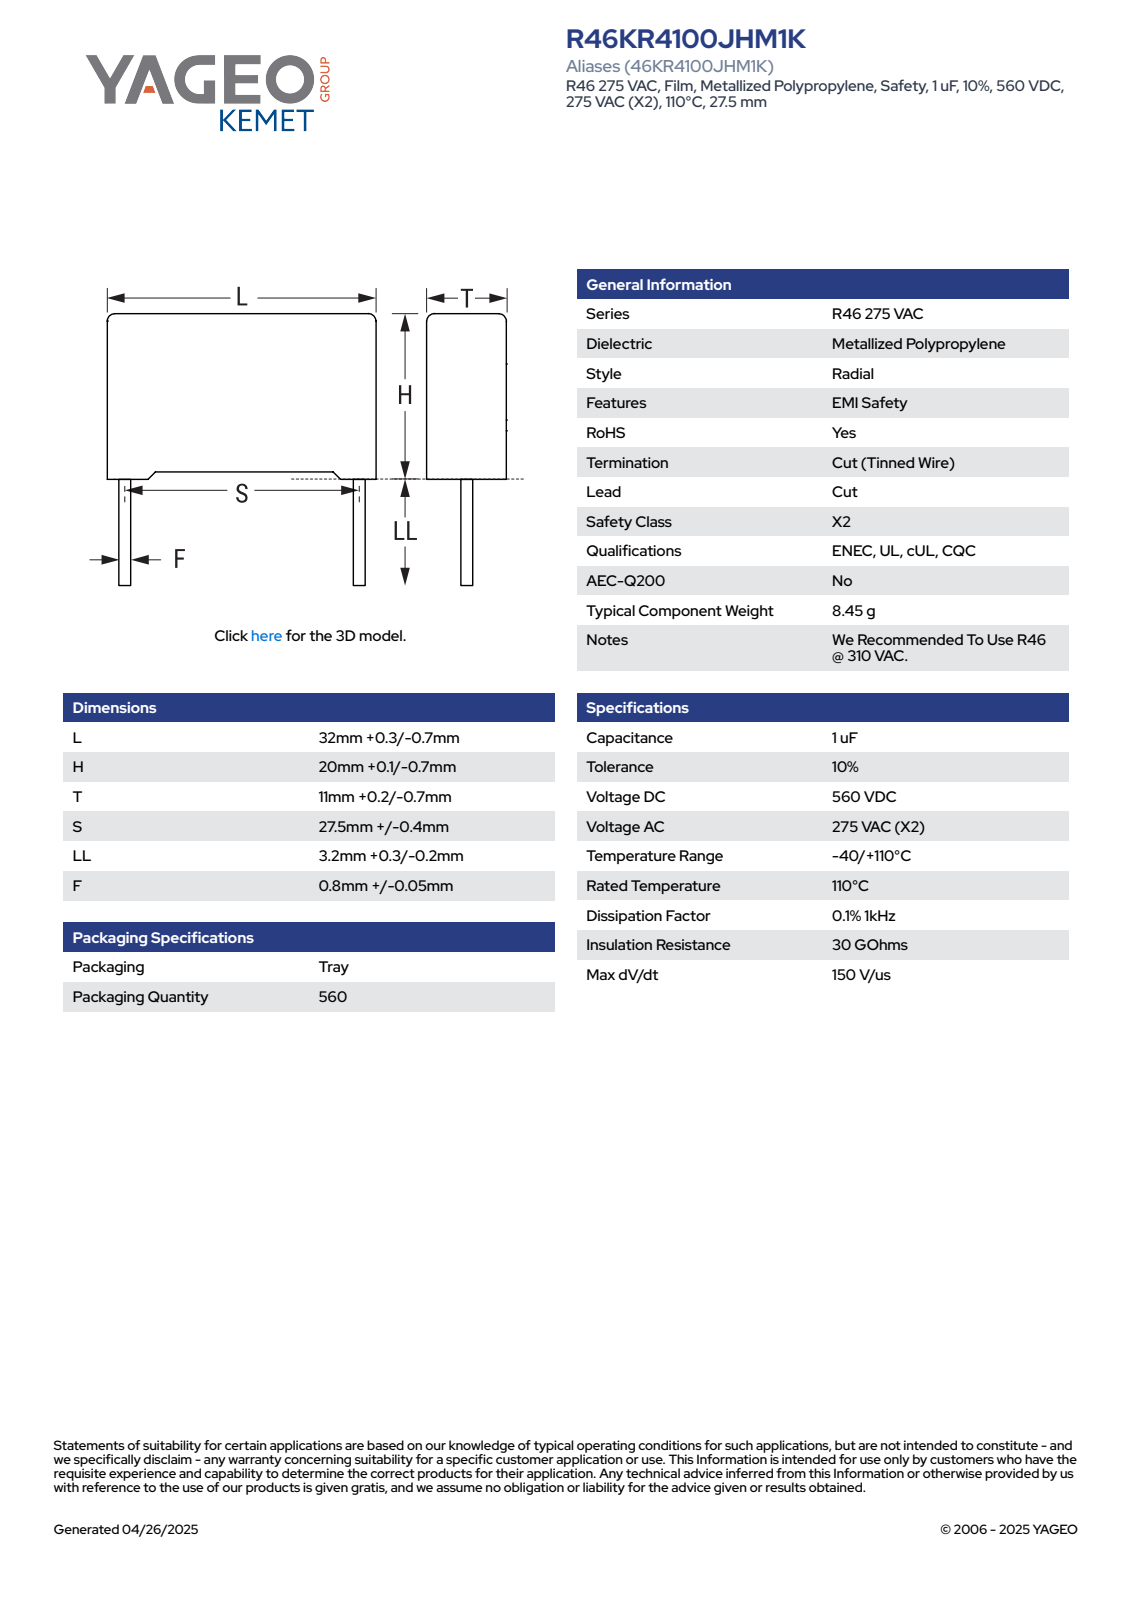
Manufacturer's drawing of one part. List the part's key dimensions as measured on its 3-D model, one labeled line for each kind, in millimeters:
Part name (STEP PRODUCT): CFR_RB2_32X20X11_L32.3H20.1T11.2S27.5LL3.5F0.85
STEP written by: SolidWorks 2021 (AUTOMOTIVE_DESIGN)
Units: millimetres
Bodies: 4 solids, 85 faces (77 planar, 8 cylindrical, 0 other)
Overall size (bounding box): 32.3 × 23.6 × 11.21
Volume: 7 032 mm³ · Surface area: 2 549 mm²
Round bosses / shafts (diameter × count): ⌀0.85 ×2
Partial cylindrical surfaces — rounded edges, fillets, slot ends (radius × count): R0.5 ×4
Main face-to-face distances: 11.2, 19.35, 32.3, 19.41, 0.69, 0.75, 20.1, 1.08, 11.21, 31.22
